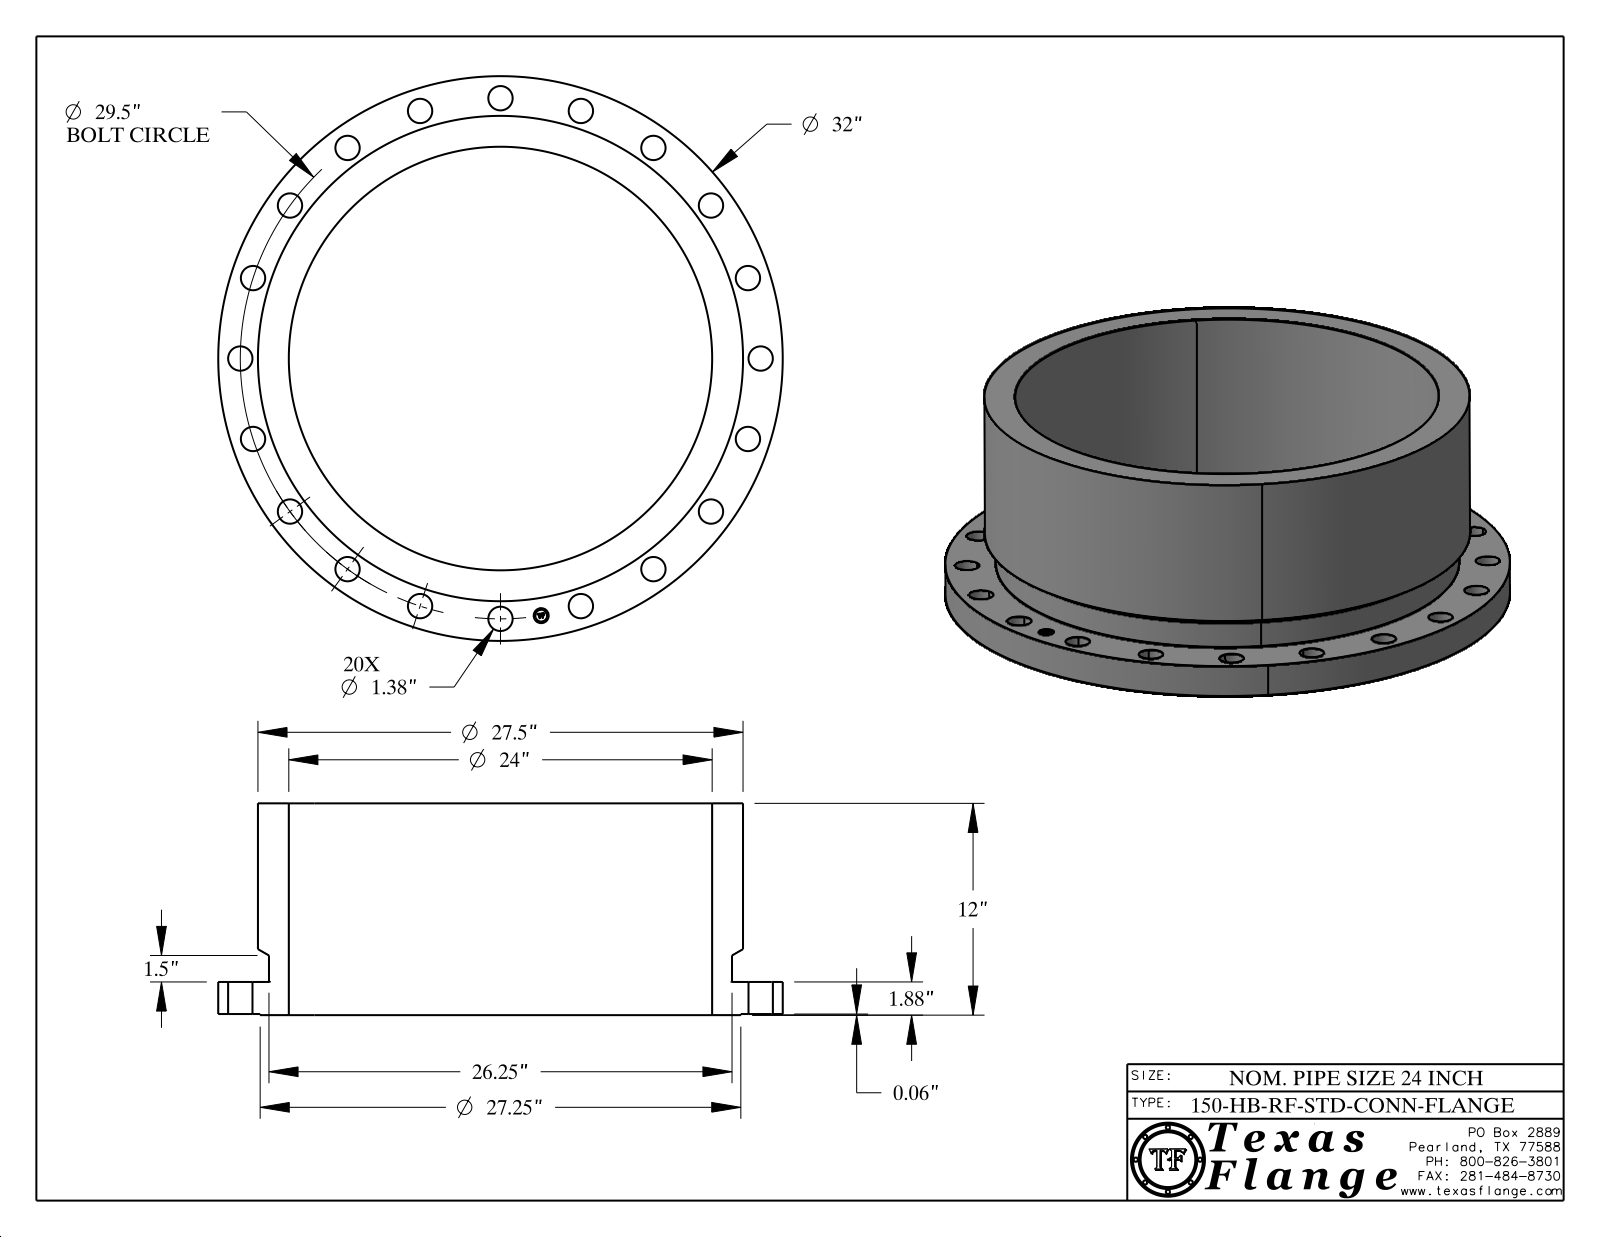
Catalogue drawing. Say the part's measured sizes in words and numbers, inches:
The part is named "24-150-HB-RF-STD-CONN-FLANGE". Its 3-D file was written by "CATIA V5 STEP AP214 (AUTOMOTIVE_DESIGN)". It is 1 solid with 445 faces: 369 planar, 70 cylindrical and 6 other. Overall it measures 32 by 32 by 12 inches. Its volume is 1 937 cubic inches and its surface area 2 849 square inches. Round holes: 20 of diameter 1.38, 1 of diameter 0.85, 1 of diameter 24. Round bosses or shafts: 8 of diameter 0.051, 1 of diameter 32, 1 of diameter 27.5, 1 of diameter 27.25, 1 of diameter 26.25, 1 of diameter 0.67. The main face-to-face distances are 1.817, 11.937, 10.12, 0.063, 1.88, 12, 1.875, 1.813, 10.125, 0.254. The hole center spacings are 14.75, 29.137, 4.615, 17.34, 20.859, 23.866, 26.285, 9.116.
